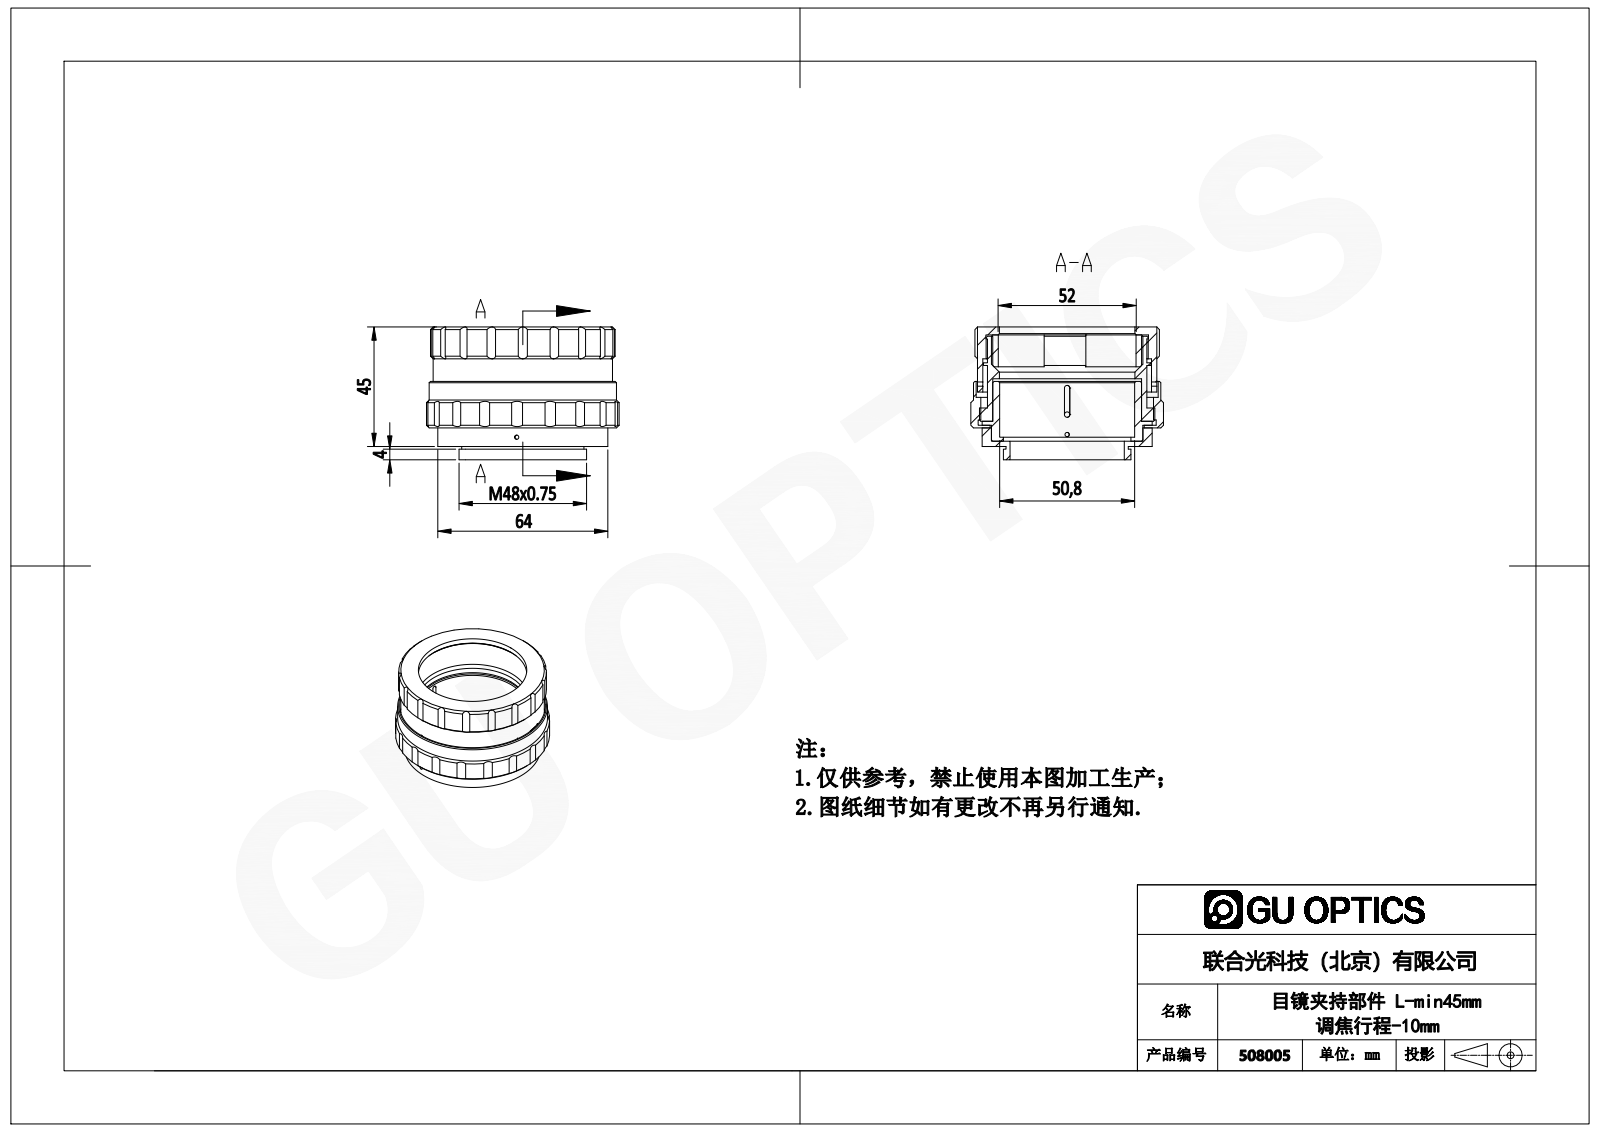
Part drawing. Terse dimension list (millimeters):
name: 508005
written by: SolidWorks 2020 (CONFIG_CONTROL_DESIGN)
unit: mm
bodies: 6 solids, 274 faces (35 planar, 180 cylindrical, 59 other)
size: 72.5 × 72.5 × 50
volume: 70 389 mm³; area: 61 685 mm²
holes: 7× ⌀1.6, 1× ⌀2.05, 1× ⌀43, 1× ⌀48, 1× ⌀50.8, 1× ⌀51, 1× ⌀51.85, 1× ⌀56, 1× ⌀58, 1× ⌀61.2, 1× ⌀63.5, 1× ⌀65
bosses: 1× ⌀70.5, 1× ⌀67.5, 1× ⌀66, 1× ⌀64, 1× ⌀63, 1× ⌀61, 1× ⌀60, 1× ⌀57
rounds: 18× R2, 18× R5, 2× R1, 1× R34.75, 1× R36.25
face distances: 5, 6, 7.5, 7, 1.5, 1, 2, 23.5, 38, 2.5
